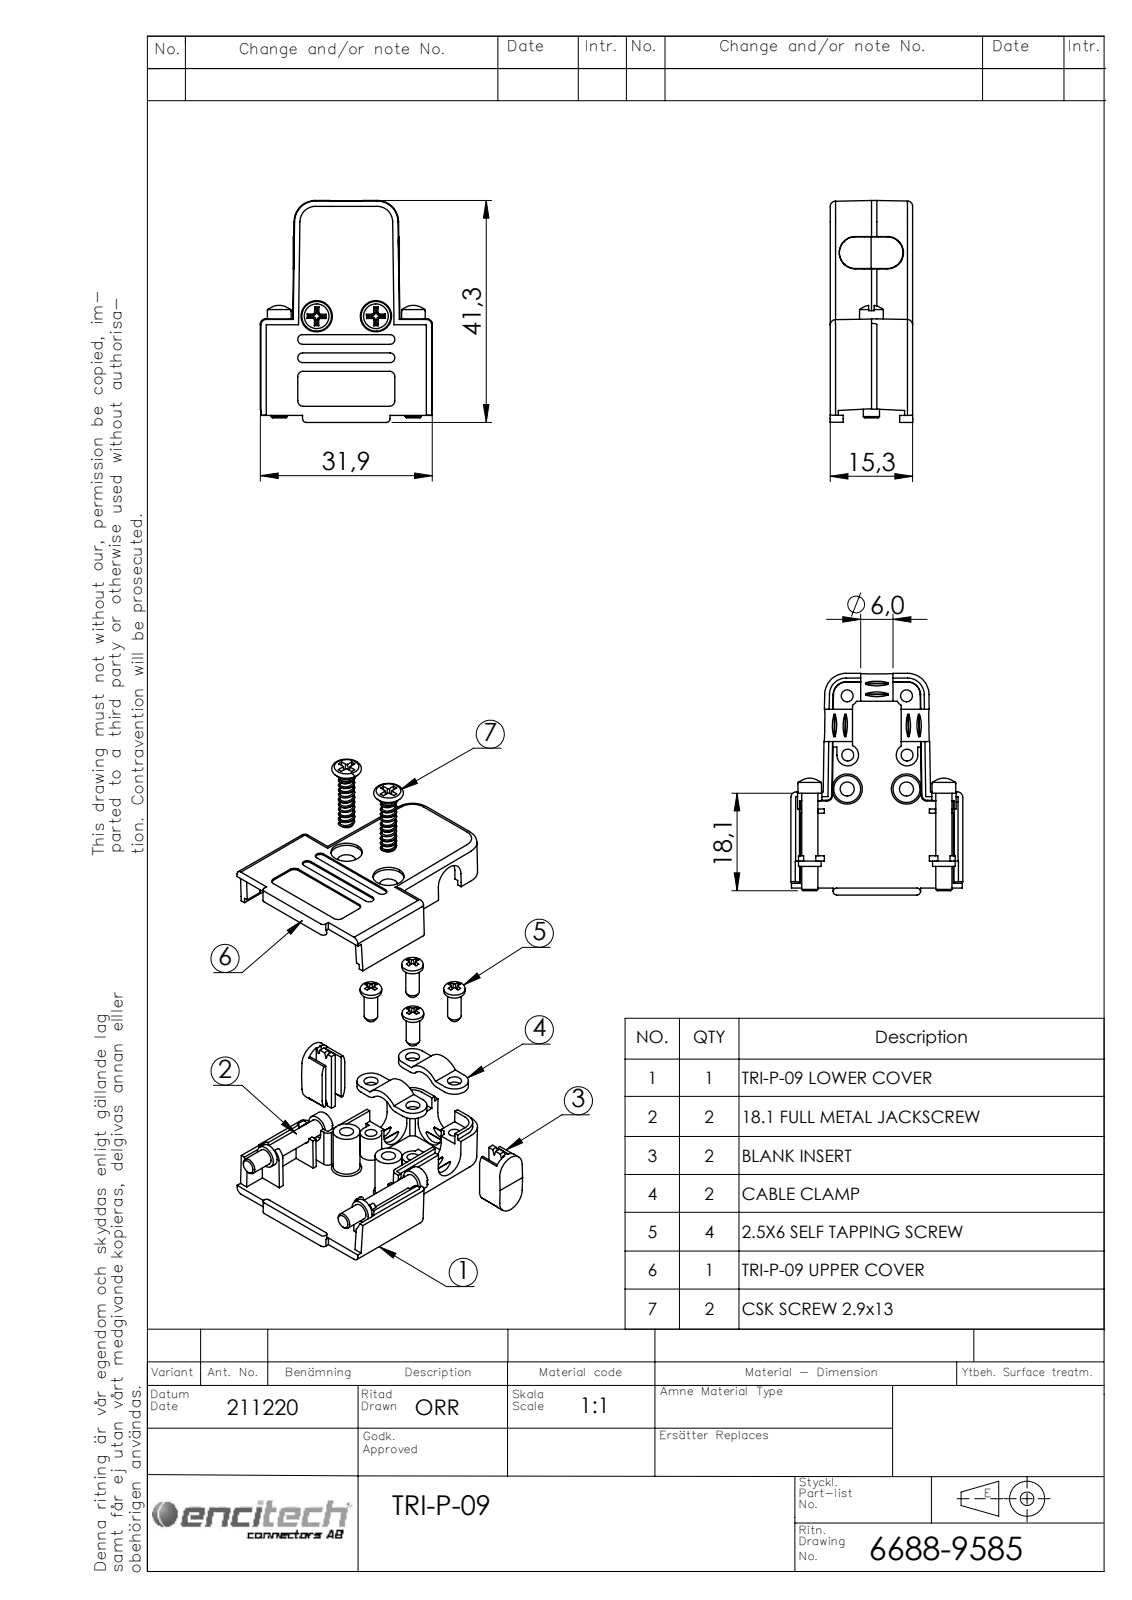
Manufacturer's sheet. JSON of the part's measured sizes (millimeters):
{"part_name": "6805-0104-01; 6855-0109-04; 6805-0104-11; 6826-0133-01 (+4 more)", "step_written_by": "SolidWorks 2021 (AUTOMOTIVE_DESIGN)", "units": "millimeters", "bodies": {"solids": 14, "faces": 807, "planar": 453, "cylindrical": 246, "other": 108}, "overall_size": [41.21, 31.9, 15.35], "volume_mm3": 6654, "surface_area_mm2": 10672, "round_holes": [[2.6, 6], [2.2, 4], [3.2, 2], [3.3, 2], [4.5, 2], [5, 2], [5.8, 2]], "round_bosses_or_shafts": [[4, 4], [3, 4], [2.5, 4], [6, 2], [4.4, 2], [4.2, 2], [2.46, 2]], "partial_cylinders_radius": [[1, 29], [0.9, 8], [0.25, 4], [0.36, 4], [0.65, 4], [0.8, 4], [2, 4], [2.6, 4]], "face_to_face_distances": [1.5, 13.8, 1.6, 15.3, 12.3, 15, 1.2, 13.5, 1, 7.5], "hole_center_spacings": [11, 6.3, 17.3, 20.5, 12.59, 12.76, 15.49, 15.63]}
